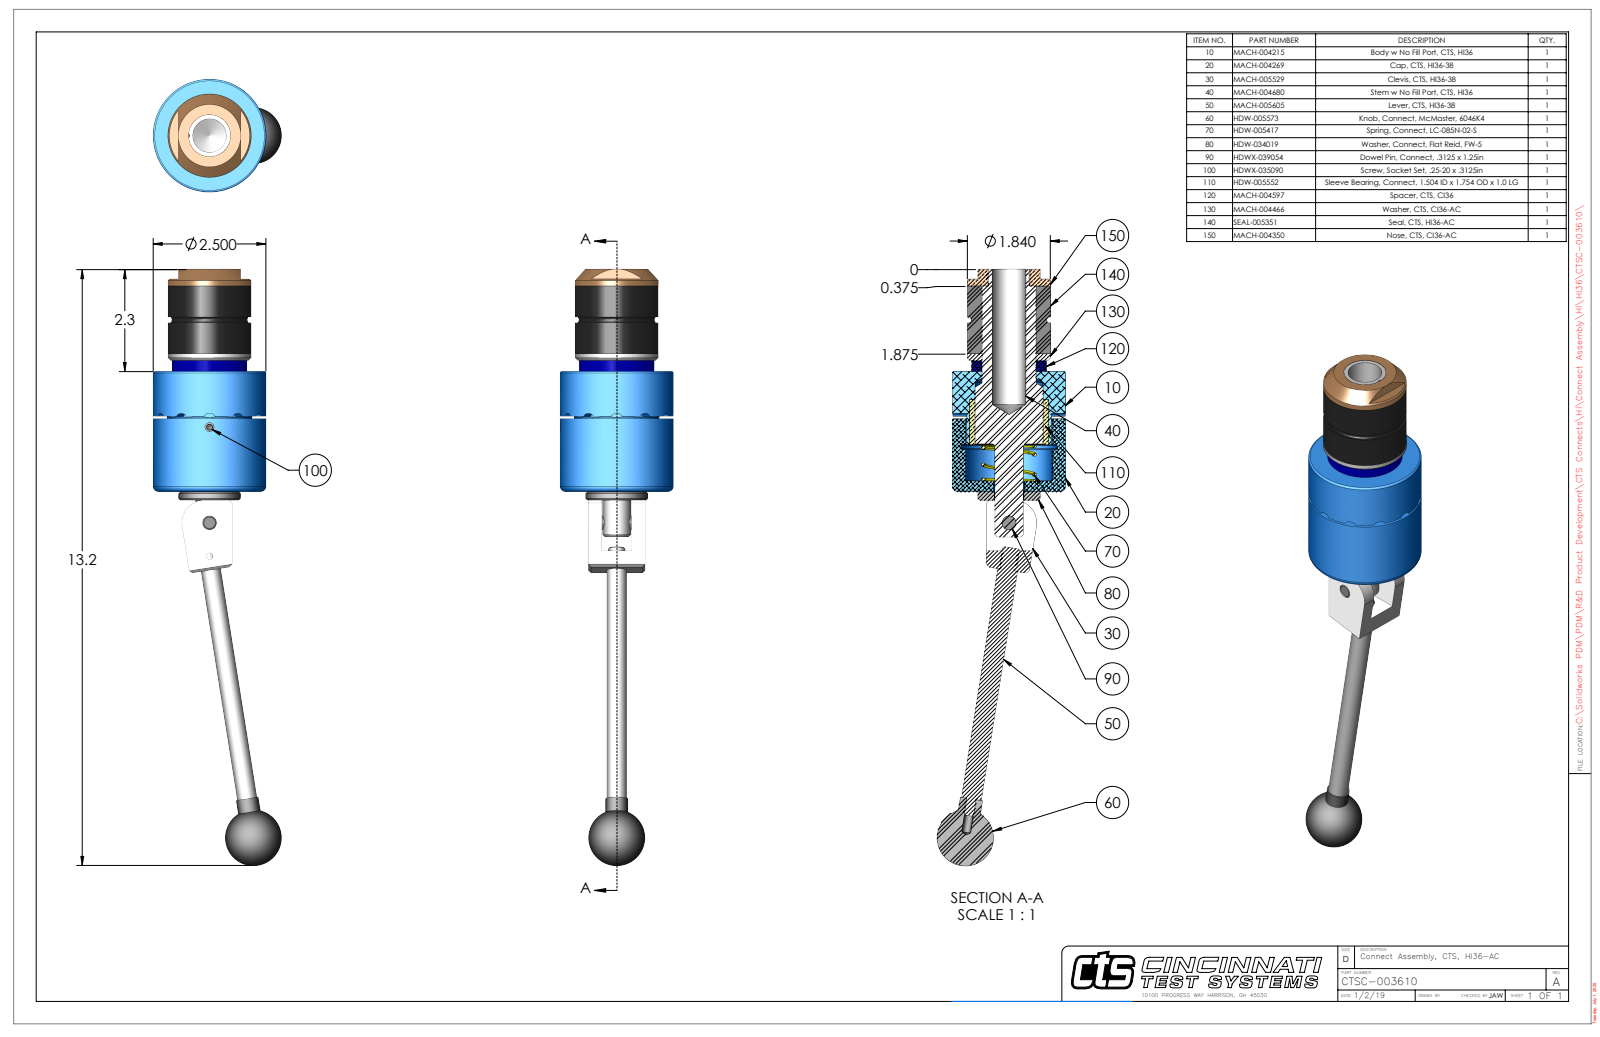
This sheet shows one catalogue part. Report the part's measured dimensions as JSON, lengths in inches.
{"part_name": "CTSC-003610", "step_written_by": "SolidWorks 2023 (AUTOMOTIVE_DESIGN)", "units": "inches", "bodies": {"solids": 10, "faces": 271, "planar": 97, "cylindrical": 107, "other": 67}, "overall_size": [13.215, 2.843, 2.5], "volume_in3": 20.8, "surface_area_in2": 116.6, "round_holes": [[0.201, 2], [0.15, 1], [0.311, 1], [0.313, 1], [0.314, 1], [0.656, 1], [0.696, 1], [0.75, 1], [0.922, 1], [1.188, 1], [1.19, 1], [1.195, 1]], "round_bosses_or_shafts": [[2.5, 1], [1.875, 1], [1.84, 1], [1.656, 1], [1.38, 1], [1.186, 1], [1, 1], [0.904, 1]], "partial_cylinders_radius": [[0.12, 12], [0.029, 2], [0.5, 1], [1.174, 1]], "face_to_face_distances": [2.668, 4.555, 1.887, 3.055, 0.387, 1.5, 0.237, 2.905, 0.15, 1.65], "hole_center_spacings": [0.74, 2.118, 2.858]}
